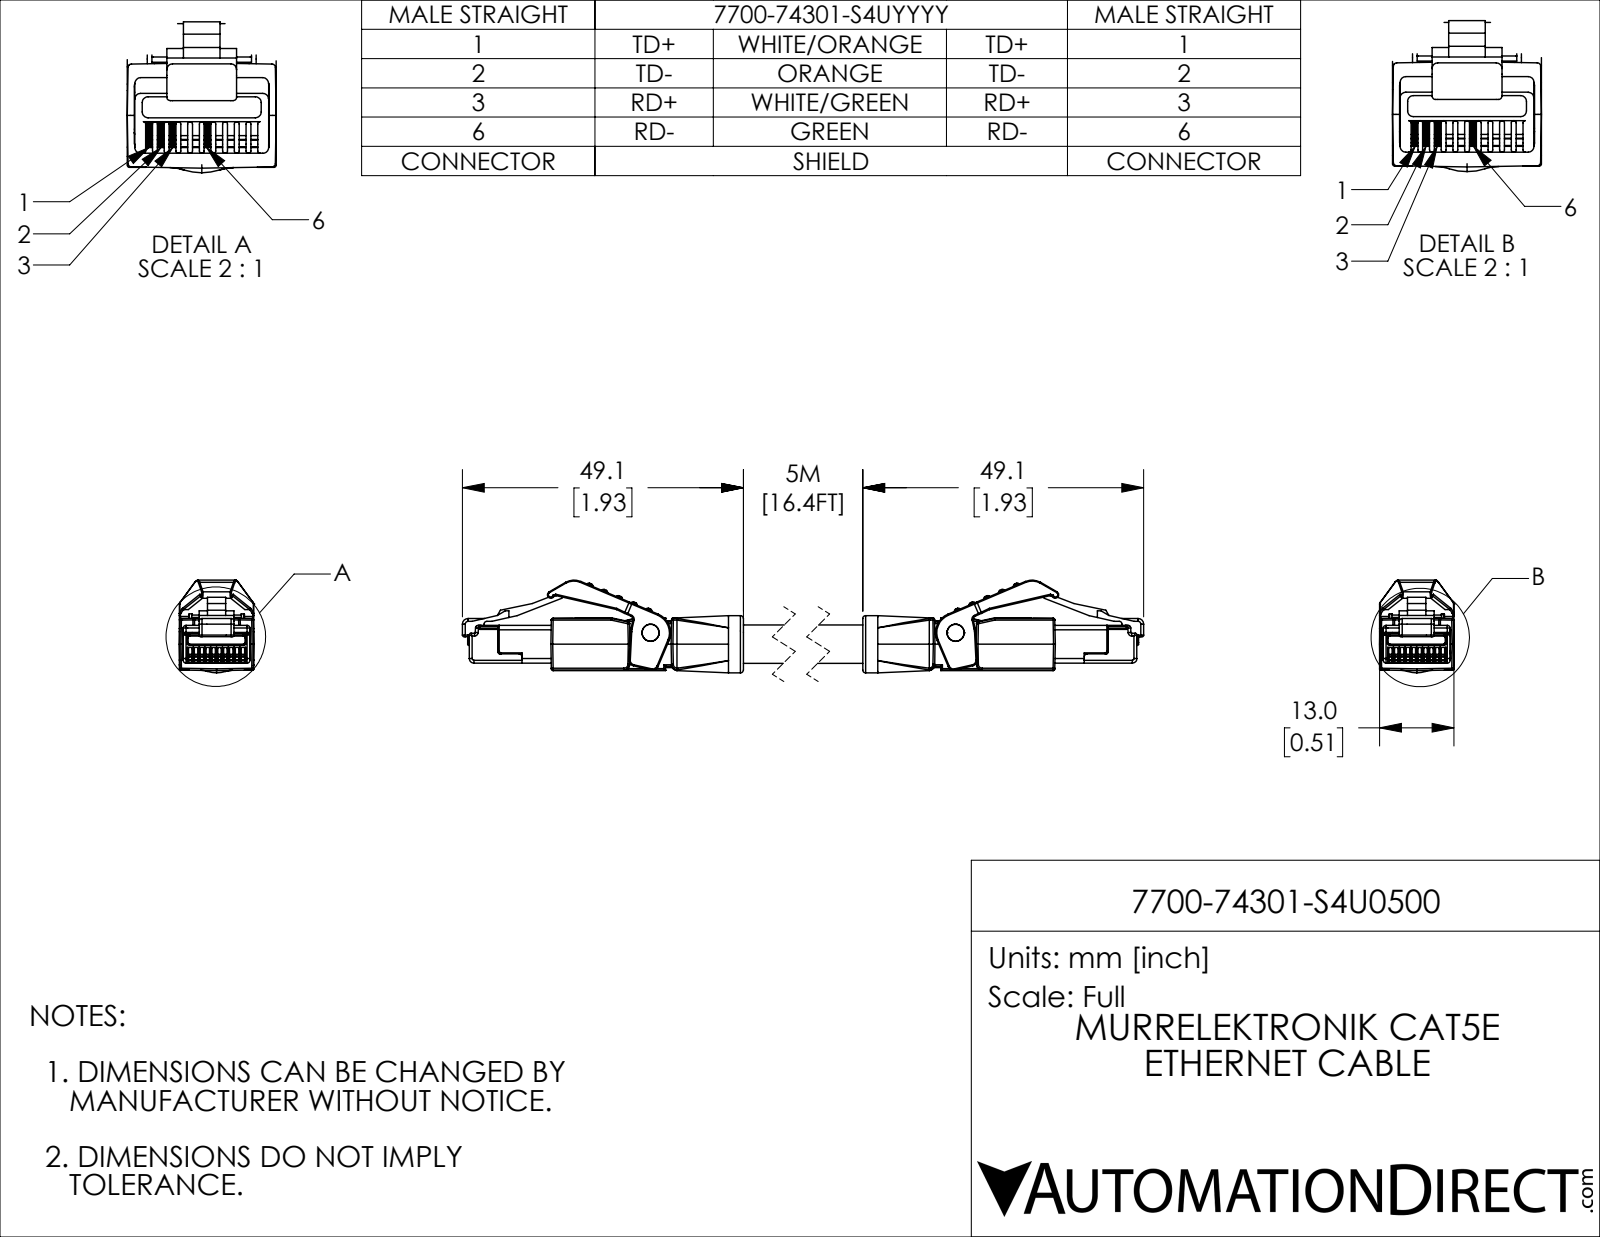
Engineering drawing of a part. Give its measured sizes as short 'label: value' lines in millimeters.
name: 7700-74301-S4U0500_1; 7700-74301-S4U0500
written by: SolidWorks 2021 (CONFIG_CONTROL_DESIGN)
unit: mm
bodies: 2 solids, 1406 faces (568 planar, 566 cylindrical, 272 other)
size: 129.8 × 16.2 × 13
volume: 10 900 mm³; area: 6 981 mm²
holes: 2× ⌀3
bosses: 2× ⌀3, 1× ⌀10, 1× ⌀6.7
rounds: 136× R0.2, 114× R0.3, 40× R0.1, 36× R0.5, 10× R1, 6× R0.8, 4× R2, 4× R5
face distances: 13, 9.2, 0.6, 12.4, 0.7, 6.6, 1.8, 11.3, 1.1, 10.6
hole spacings: 64.2
